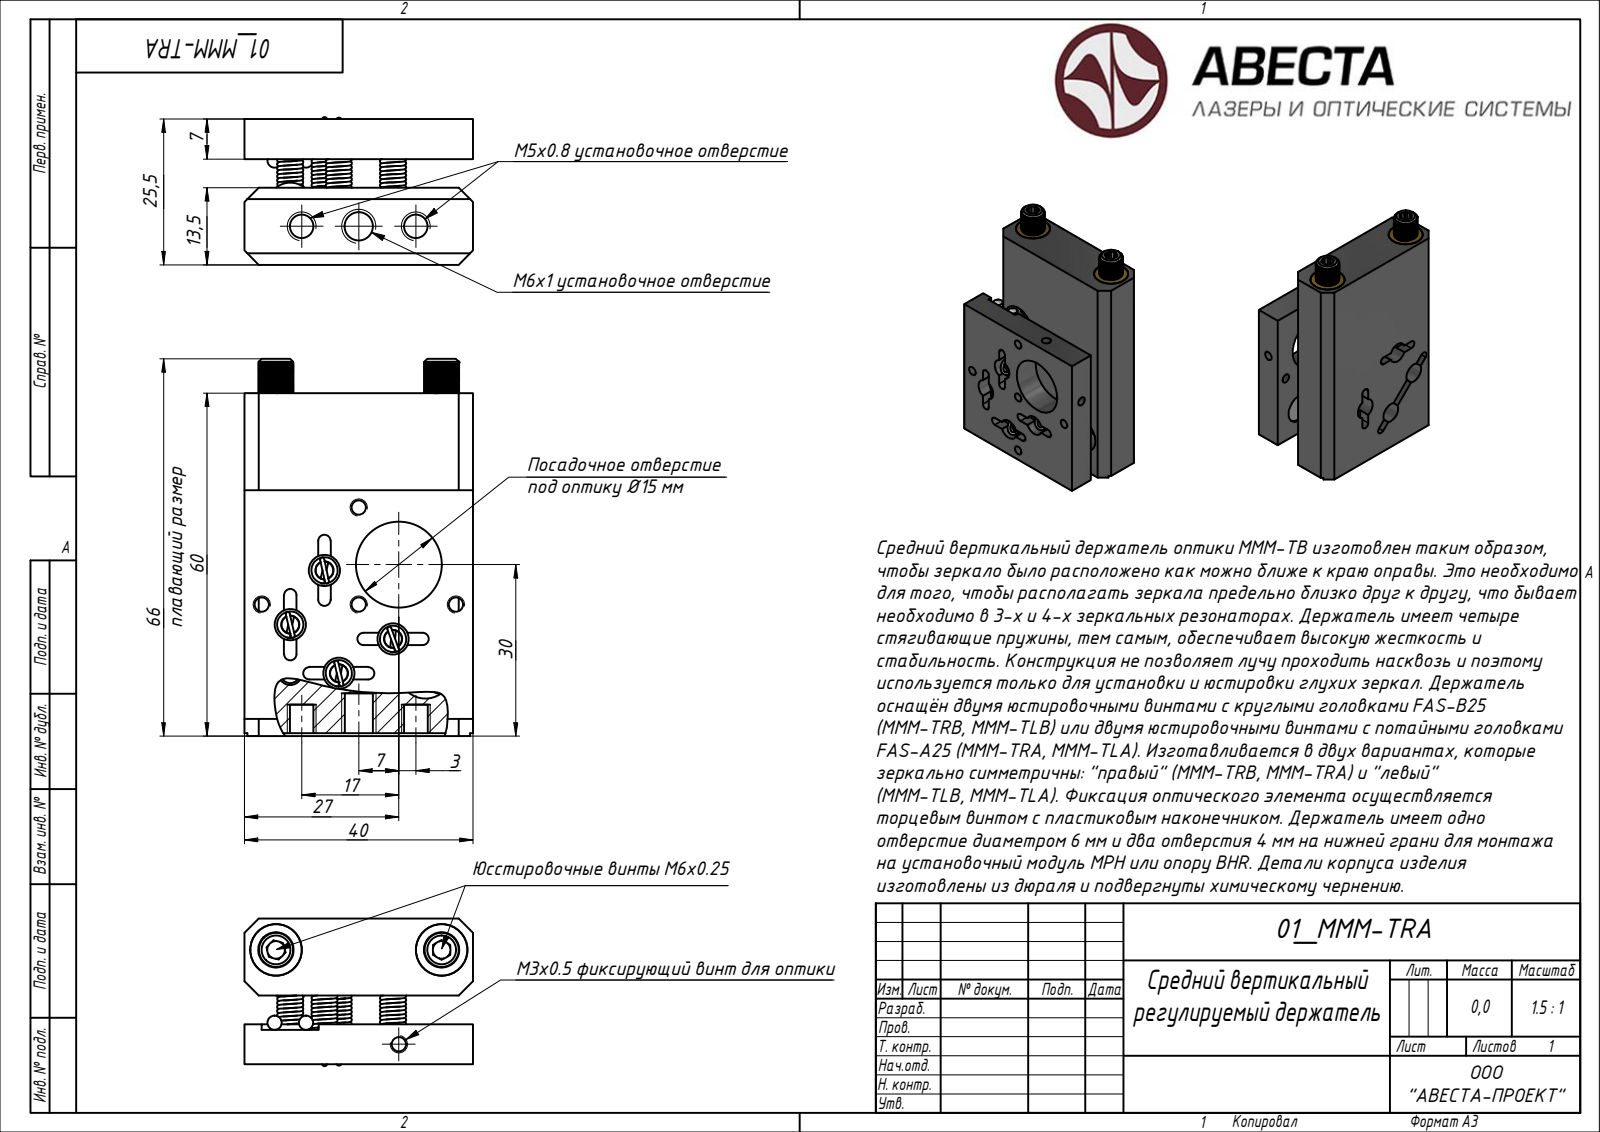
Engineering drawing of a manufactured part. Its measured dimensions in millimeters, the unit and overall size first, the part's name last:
Units: millimetres
Overall size (bounding box): 70 × 40 × 25.5
Main face-to-face distances: 13.5, 12, 25.5, 7, 5, 18.5, 40, 2.5, 34.29, 3
Volume: 35 954 mm³ · Surface area: 19 157 mm²
Bodies: 9 solids, 276 faces (126 planar, 0 cylindrical, 150 other)
STEP written by: ST-DEVELOPER v15 (AUTOMOTIVE_DESIGN)
